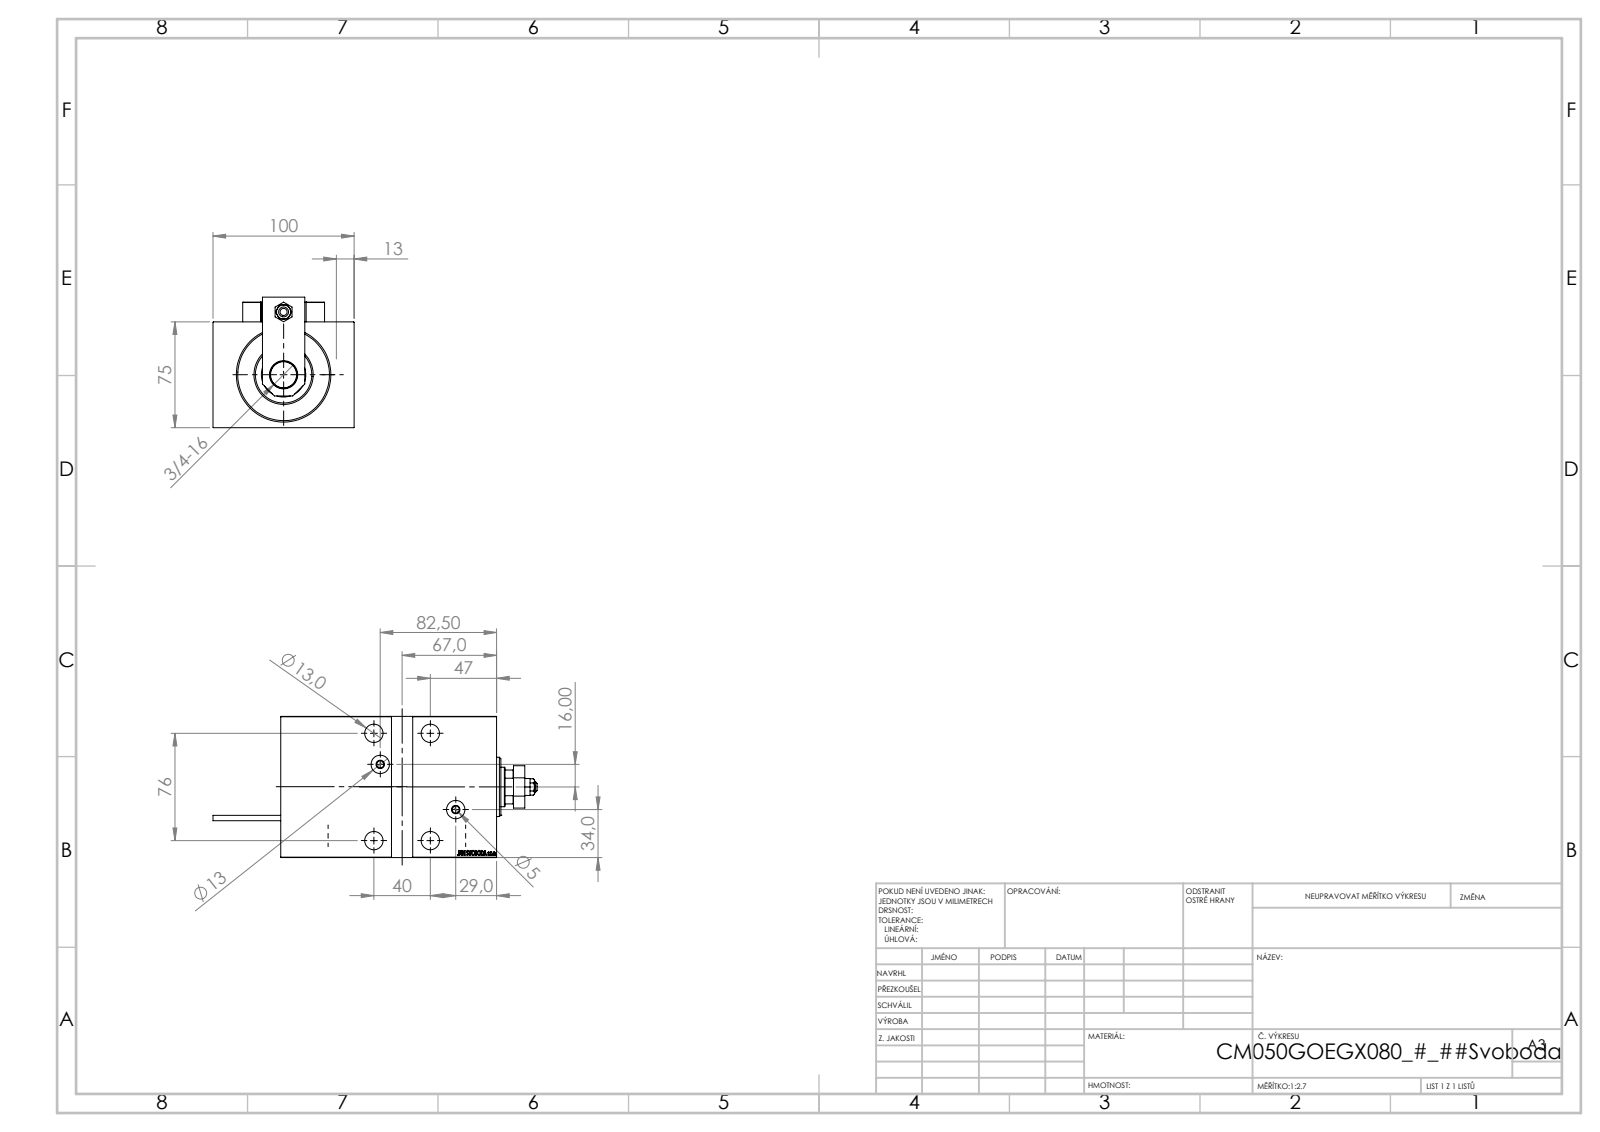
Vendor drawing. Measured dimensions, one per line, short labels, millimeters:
name: MAGNET; KONCOVKA; SWITCH X; TYC_L79 (+7 more)
written by: SolidWorks 2019 (CONFIG_CONTROL_DESIGN)
unit: mm
bodies: 26 solids, 1333 faces (602 planar, 186 cylindrical, 545 other)
size: 229.7 × 100 × 92.5
volume: 1 031 000 mm³; area: 163 785 mm²
holes: 6× ⌀13, 5× ⌀8, 4× ⌀3.2, 4× ⌀4, 4× ⌀5, 4× ⌀19, 1× ⌀7, 1× ⌀18.5, 1× ⌀20, 1× ⌀28, 1× ⌀31.5, 1× ⌀50
bosses: 2× ⌀18, 2× ⌀6, 2× ⌀5, 2× ⌀3.8, 1× ⌀42, 1× ⌀13, 1× ⌀11
rounds: 30× R0.3, 2× R3, 1× R13.5
face distances: 75, 100, 14, 5, 153, 139, 148, 134, 12, 17
hole spacings: 11.37, 20, 29.59, 29.69, 36.06, 40, 42.19, 48.83
